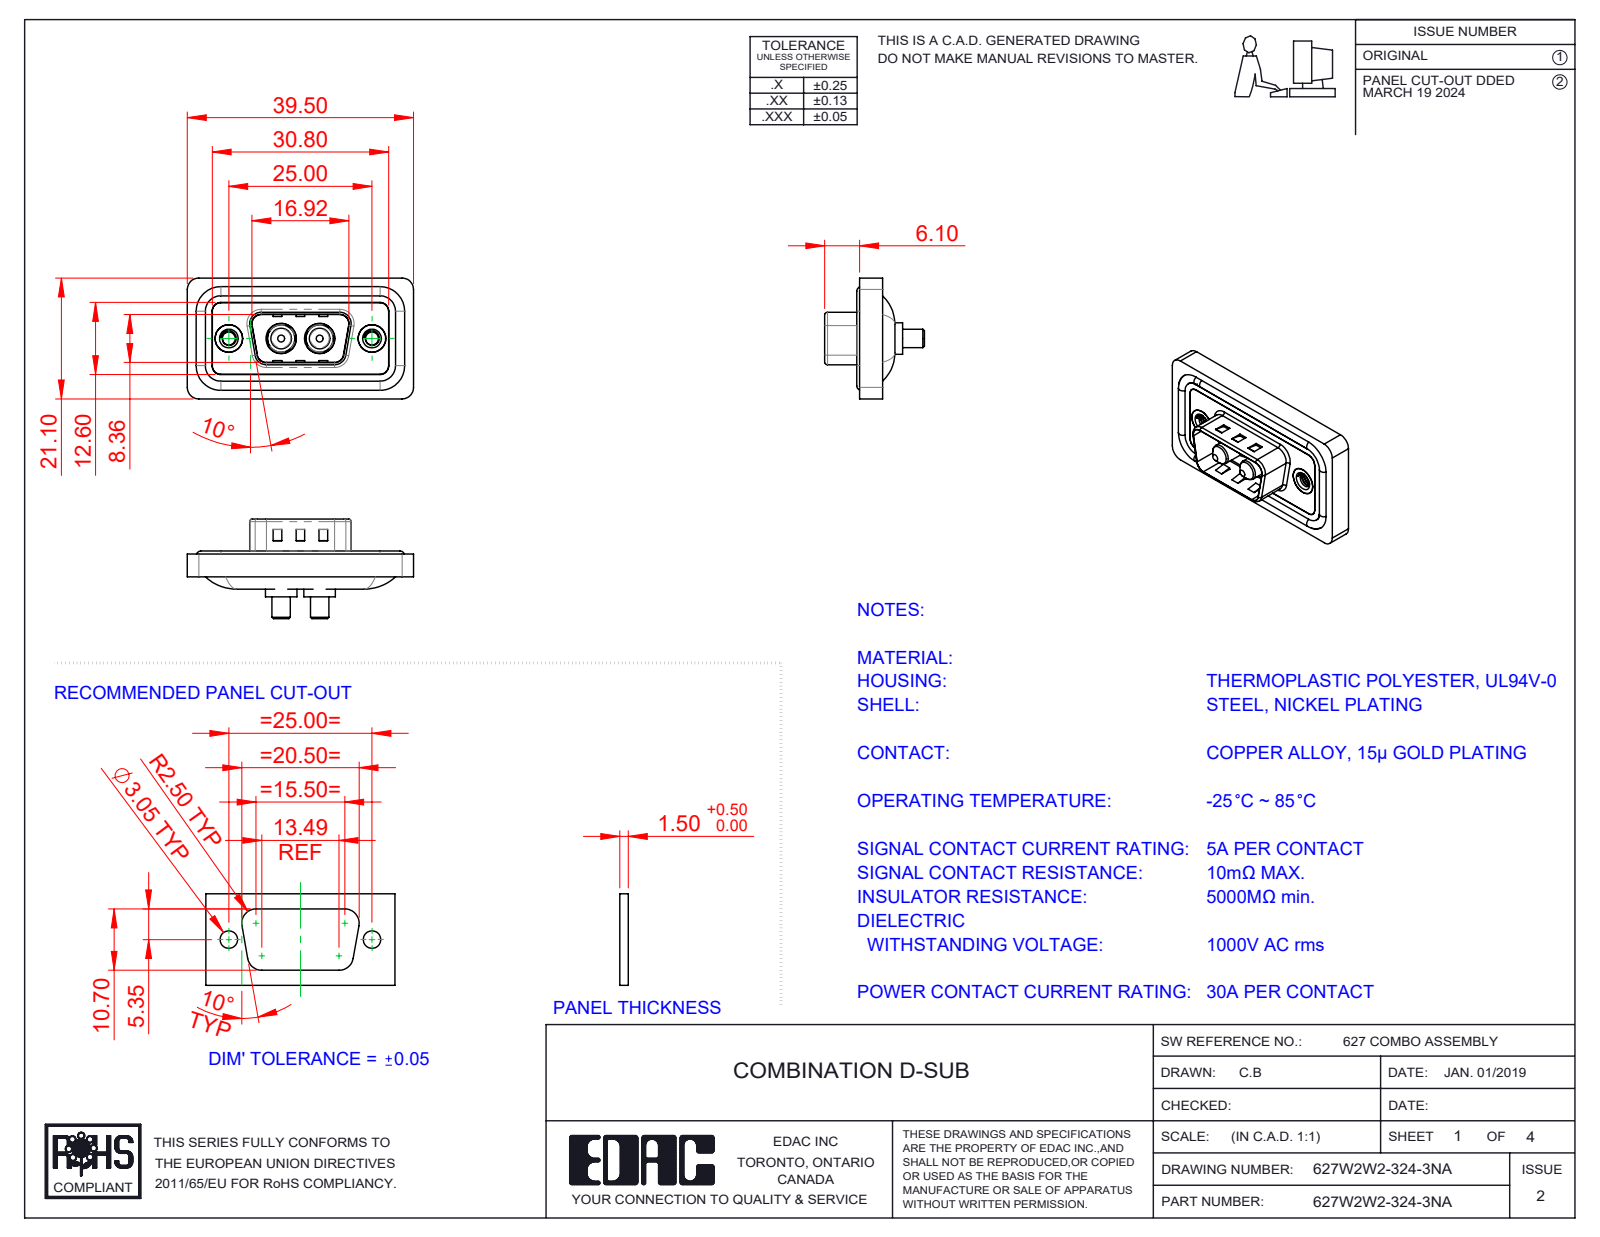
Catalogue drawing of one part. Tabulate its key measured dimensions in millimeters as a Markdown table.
| quantity | value |
| --- | --- |
| part name | 627W2W2-324-3NA; 627Combo Threaded Rivet_A; 627Combo Waterproof Housing_09 Contacts; 627Combo Housing_2W2 (+3 more) |
| STEP written by | SolidWorks 2023 (CONFIG_CONTROL_DESIGN) |
| units | millimeters |
| bodies | 11 solids, 487 faces (165 planar, 220 cylindrical, 102 other) |
| overall size | 39.5 × 21.1 × 17.4 |
| volume | 4 476 mm³ |
| surface area | 6 991 mm² |
| round holes (diameter × count) | 2.26 × 2, 4 × 2, 4.8 × 2, 4.85 × 2, 5 × 2, 5.3 × 2 |
| round bosses / shafts (diameter × count) | 1.6 × 4, 5.5 × 2, 5.2 × 2, 4.9 × 2, 4.75 × 2, 3.75 × 2, 3.6 × 2, 3.2 × 2 |
| partial cylindrical surfaces (radius × count) | 1.5 × 22, 2 × 18, 0.5 × 8, 1.6 × 8, 0.25 × 4, 0.6 × 4, 0.65 × 4, 0.9 × 4 |
| main face-to-face distances | 0.4, 1.1, 2.9, 3.1, 0.5, 1.6, 1.5, 4, 2.5, 0.7 |
| hole center spacings | 9.14, 15.86, 6.72, 25 |
